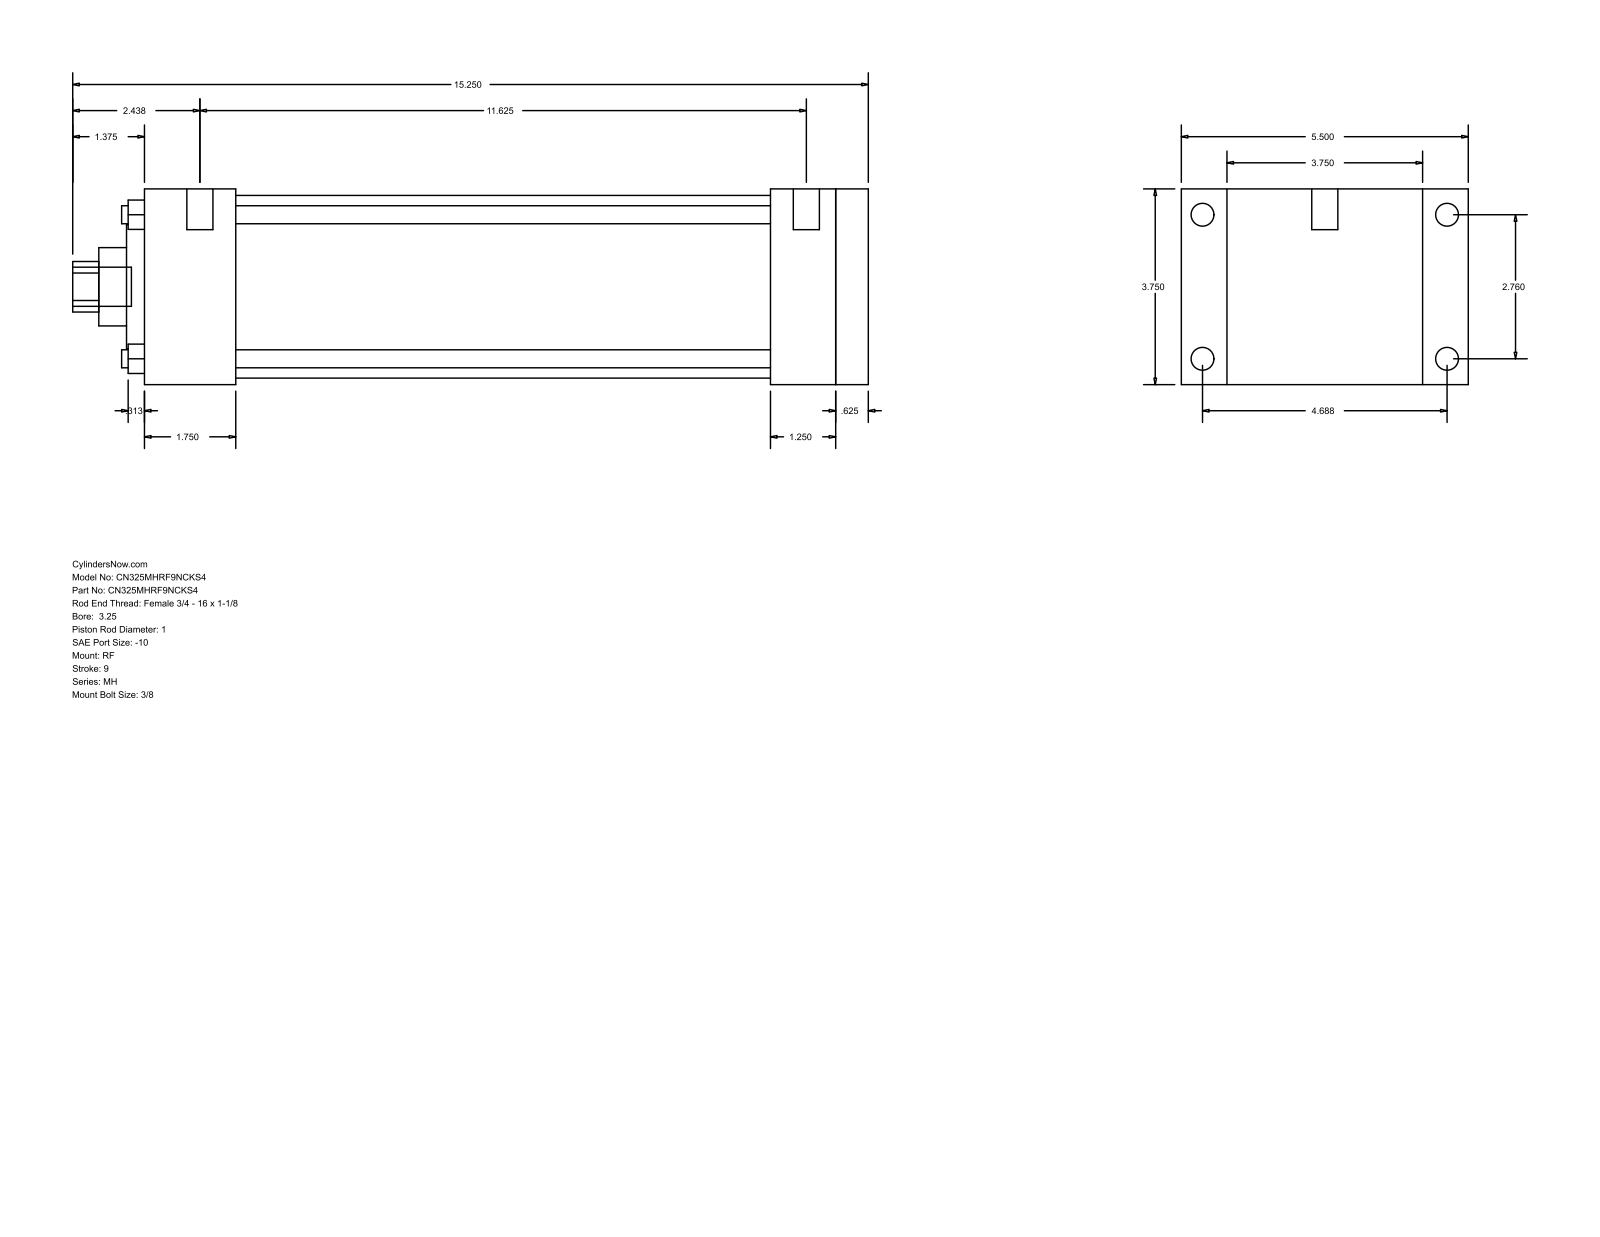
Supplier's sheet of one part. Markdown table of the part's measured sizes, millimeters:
| quantity | value |
| --- | --- |
| part name | MH_RF__0325_1 |
| STEP written by | GSSL Pune (CONFIG_CONTROL_DESIGN) |
| units | millimeters |
| bodies | 0 solids, 94 faces (65 planar, 29 cylindrical, 0 other) |
| overall size | 387.35 × 139.7 × 95.25 |
| round holes (diameter × count) | 8.76 × 4, 25.4 × 1, 38.1 × 1, 60.33 × 1, 88.9 × 1 |
| round bosses / shafts (diameter × count) | 11.13 × 4, 5.56 × 4, 12.7 × 2, 19.05 × 1 |
| partial cylindrical surfaces (radius × count) | 12.29 × 1 |
| main face-to-face distances | 95.24, 352.43, 15.87, 336.56, 22.23, 117.47, 44.46, 292.1, 307.97, 304.81 |
| hole center spacings | 49.57, 70.1, 99.14 |
